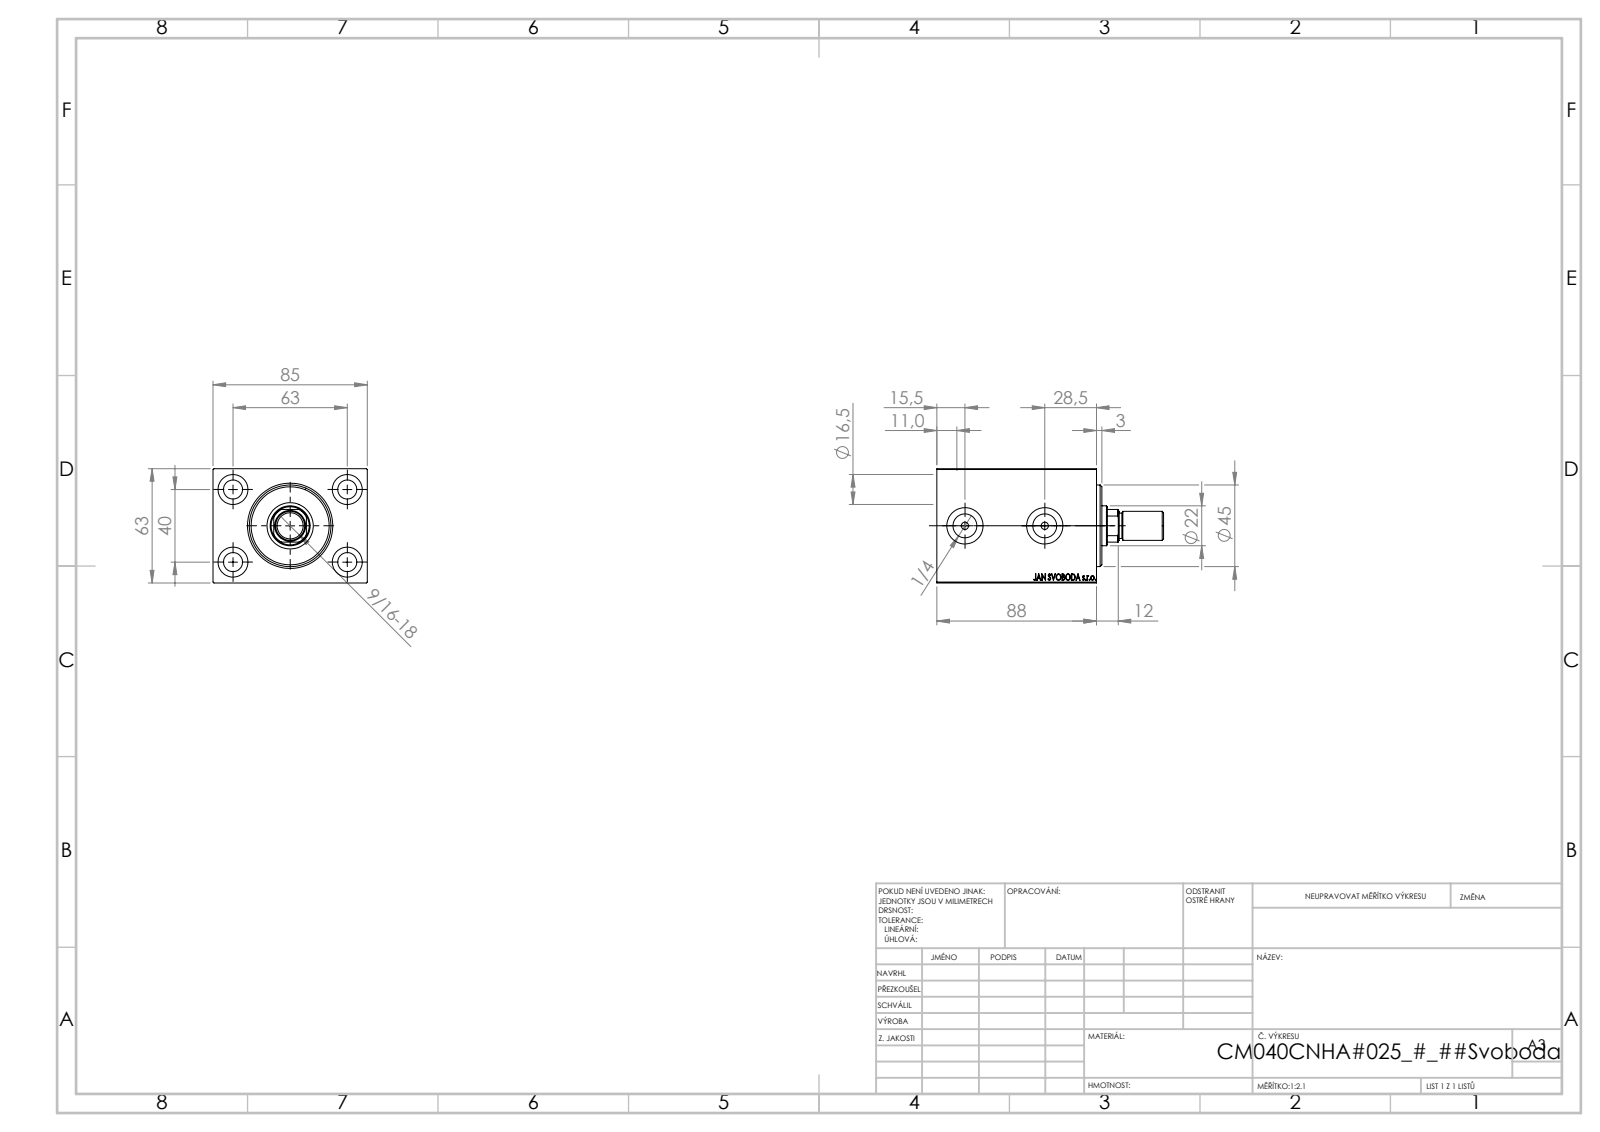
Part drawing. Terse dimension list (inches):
name: V450CM_C_Body; V450CM_MALE_METRIC; V450CM_C_VCP; V450CM_VC_B
written by: SolidWorks 2019 (CONFIG_CONTROL_DESIGN)
unit: in
bodies: 4 solids, 876 faces (412 planar, 64 cylindrical, 400 other)
size: 4.921 × 3.346 × 2.48
volume: 25.24 in³; area: 122.3 in²
holes: 4× ⌀0.413, 4× ⌀0.65, 2× ⌀0.157, 2× ⌀0.518, 2× ⌀0.787, 1× ⌀0.492, 1× ⌀0.866, 1× ⌀1.004, 1× ⌀1.575, 1× ⌀1.654, 1× ⌀1.772
bosses: 1× ⌀0.63, 1× ⌀0.551
rounds: 1× R0.413
face distances: 2.48, 3.346, 0.472, 2.992, 3.465, 1.575, 2.52, 0.433, 1.457, 0.984
hole spacings: 1.469, 1.575, 2.48, 2.938, 1.732
